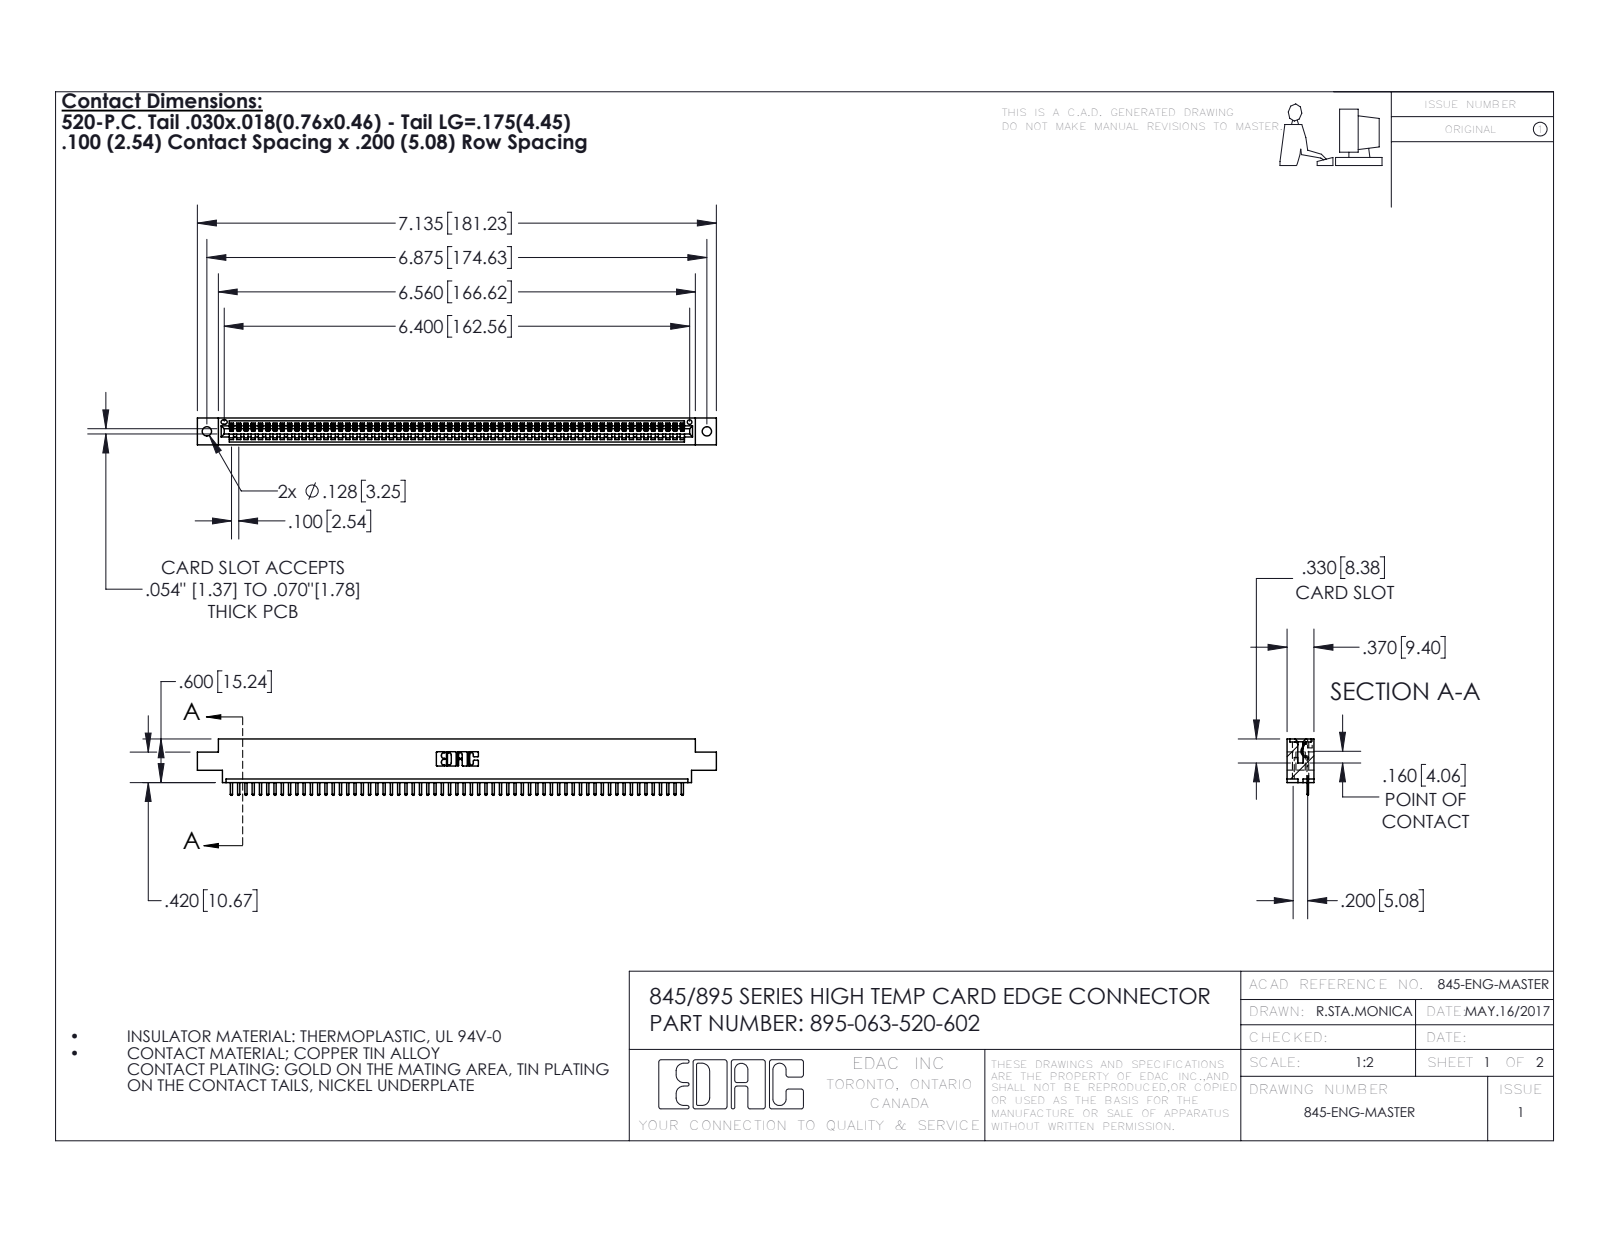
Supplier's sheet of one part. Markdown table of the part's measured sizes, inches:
| quantity | value |
| --- | --- |
| part name | 395-063-520-602; 345 Part_0.170 Offset - 0.128 Dia; 345-292-001_345-293-120 |
| STEP written by | SolidWorks 2016 (CONFIG_CONTROL_DESIGN) |
| units | inches |
| bodies | 64 solids, 4036 faces (2730 planar, 1306 cylindrical, 0 other) |
| overall size | 7.135 × 0.775 × 0.37 |
| volume | 1.041 in³ |
| surface area | 34.43 in² |
| round holes (diameter × count) | 0.128 × 2, 0.064 × 1 |
| partial cylindrical surfaces (radius × count) | 0.01 × 128, 0.006 × 126, 0.01 × 22, 0.007 × 6, 0.031 × 6, 0.026 × 3, 0.031 × 2, 0.04 × 2 |
| main face-to-face distances | 0.298, 0.072, 0.37, 0.2, 0.098, 0.272, 0.025, 0.225, 0.072, 0.175 |
| hole center spacings | 0.27, 6.639, 6.875 |
